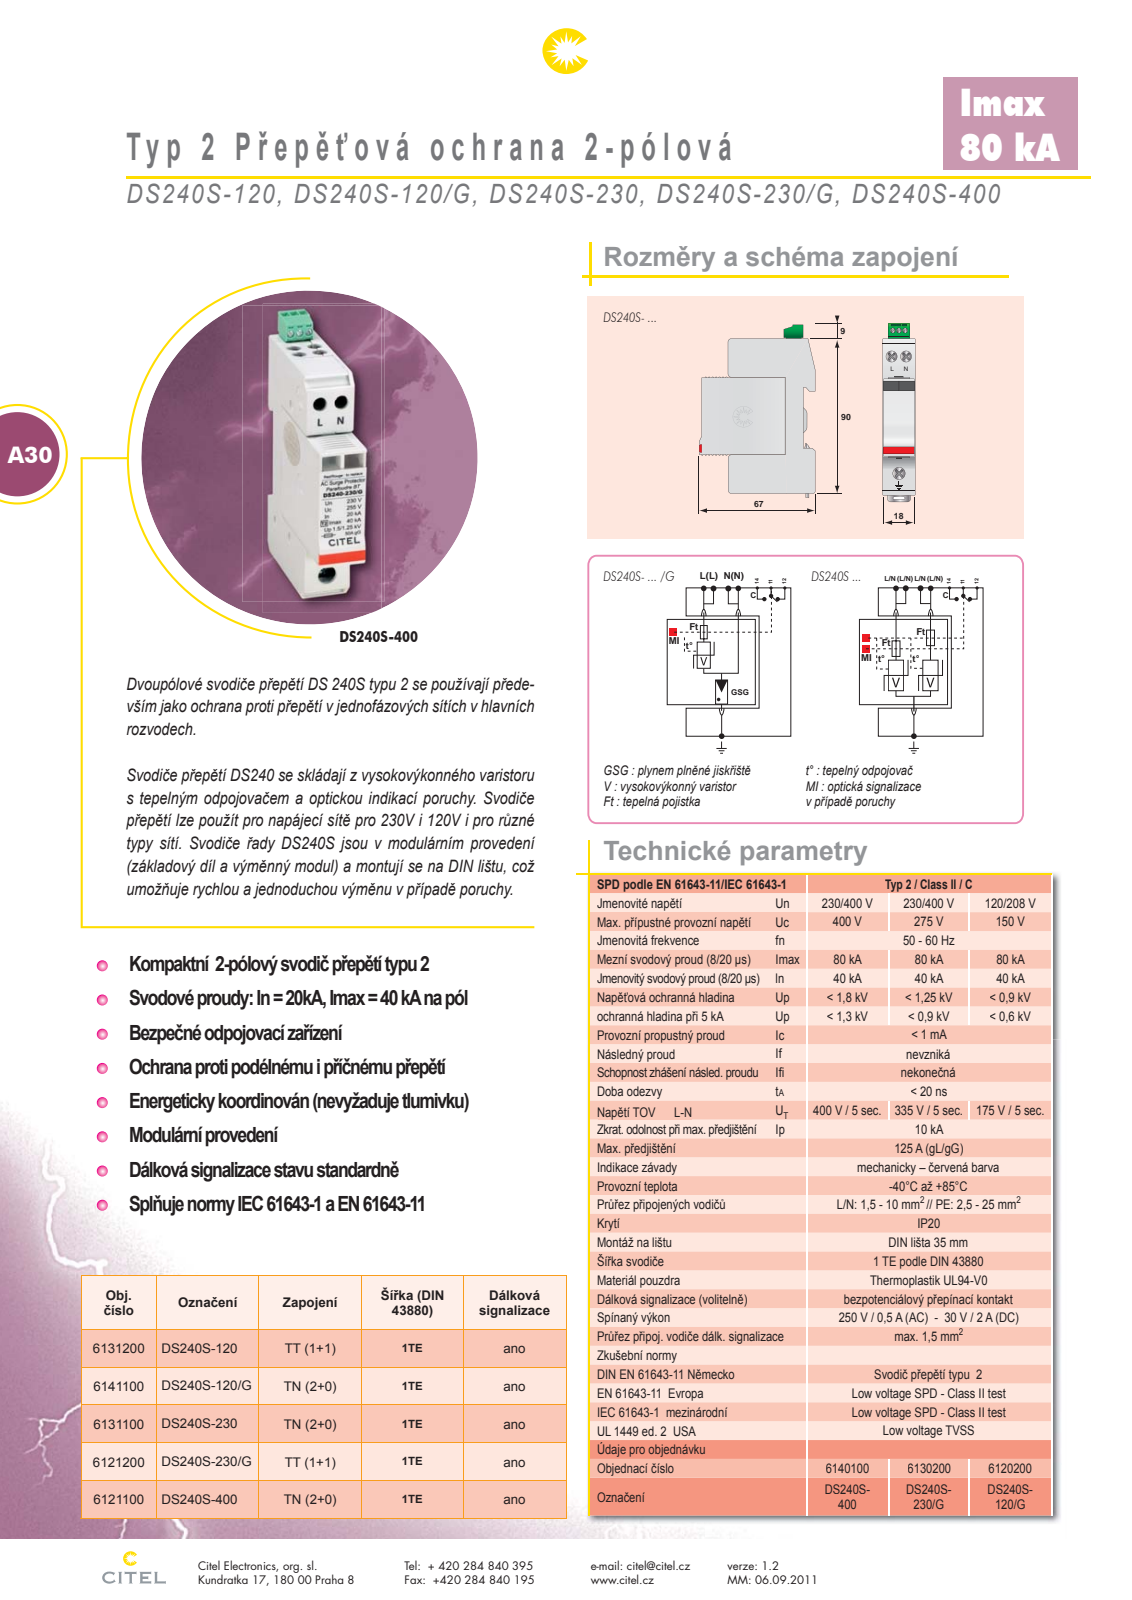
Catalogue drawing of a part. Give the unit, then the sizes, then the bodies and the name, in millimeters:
Units: millimetres
Overall size (bounding box): 105.1 × 67.8 × 17.8
Round holes (diameter × count): ⌀5.4 ×4, ⌀2.8 ×3, ⌀3.2 ×3, ⌀5 ×3, ⌀5.3 ×2, ⌀7 ×1, ⌀8.5 ×1
Round bosses / shafts (diameter × count): ⌀2.4 ×3, ⌀1.6 ×3, ⌀6.8 ×2, ⌀10 ×1, ⌀7 ×1, ⌀5 ×1
Partial cylindrical surfaces — rounded edges, fillets, slot ends (radius × count): R0.5 ×47, R1.8 ×13, R0.2 ×9, R1 ×8, R1.5 ×6, R1.56 ×6, R1.6 ×6, R0.3 ×4
Main face-to-face distances: 17.8, 17.5, 67.5, 22.5, 6.7, 44.5, 1.6, 15.5, 66.3, 67.3
Hole centre spacings: 8, 3.5, 6.7, 10.44, 15.36, 69.37, 84.67, 7
Volume: 85 590 mm³ · Surface area: 24 145 mm²
Bodies: 1 solid, 982 faces (700 planar, 197 cylindrical, 85 other)
Part name (STEP PRODUCT): DS240S
STEP written by: Creo Elements/Direct Modeling 20.0AP0401 12-May-2017 (C) Parametric Technology GmbH (AUTOMOTIVE_DESIGN)
